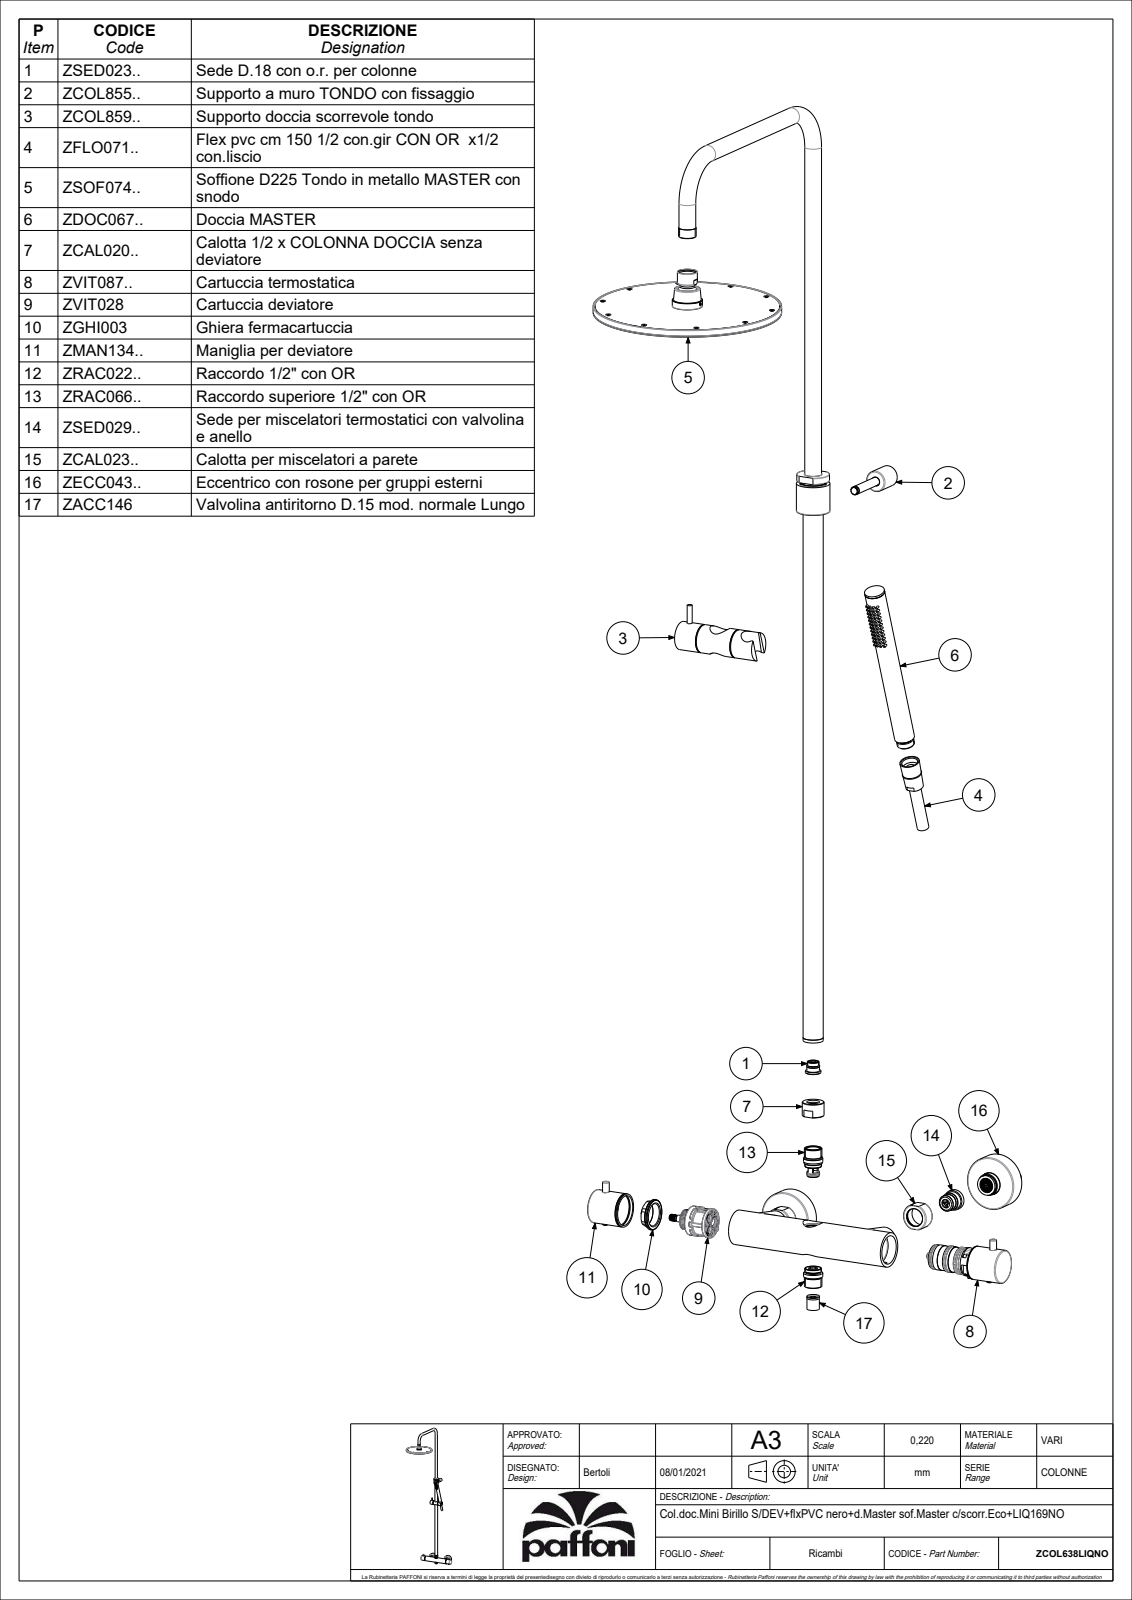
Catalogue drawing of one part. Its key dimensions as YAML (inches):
part_name: "ZCOL638LIQNO"
step_written_by: "CREO PARAMETRIC BY PTC INC, 2020044 (CONFIG_CONTROL_DESIGN)"
units: inches
bodies: {solids: 31, faces: 2996, planar: 804, cylindrical: 1449, other: 743}
overall_size: [48.626, 19.488, 11.328]
volume: 49.56
surface_area: 808.8
round_holes:
  - {diameter: 0.031, count: 324}
  - {diameter: 0.047, count: 80}
  - {diameter: 0.039, count: 50}
  - {diameter: 0.157, count: 4}
  - {diameter: 0.276, count: 3}
  - {diameter: 0.413, count: 3}
  - {diameter: 0.571, count: 3}
  - {diameter: 0.594, count: 3}
  - {diameter: 0.63, count: 3}
  - {diameter: 0.669, count: 3}
  - {diameter: 0.965, count: 3}
  - {diameter: 0.984, count: 3}
round_bosses_or_shafts:
  - {diameter: 0.945, count: 4}
  - {diameter: 1.575, count: 3}
  - {diameter: 0.787, count: 3}
  - {diameter: 2.5, count: 2}
  - {diameter: 1.063, count: 2}
  - {diameter: 0.906, count: 2}
  - {diameter: 0.835, count: 2}
  - {diameter: 0.748, count: 2}
partial_cylinders:
  - {radius: 0.059, count: 64}
  - {radius: 0.039, count: 6}
  - {radius: 0.069, count: 4}
  - {radius: 0.108, count: 2}
  - {radius: 0.157, count: 2}
  - {radius: 0.256, count: 2}
  - {radius: 0.283, count: 2}
  - {radius: 0.335, count: 2}
face_to_face_distances: [0.256, 0.118, 0.024, 1.665, 1.642, 1.76, 1.783, 0.128, 0.119, 1.504]
hole_center_spacings: [0.252, 0.424, 0.197, 0.611, 0.394, 0.803, 1.109, 3.543]
